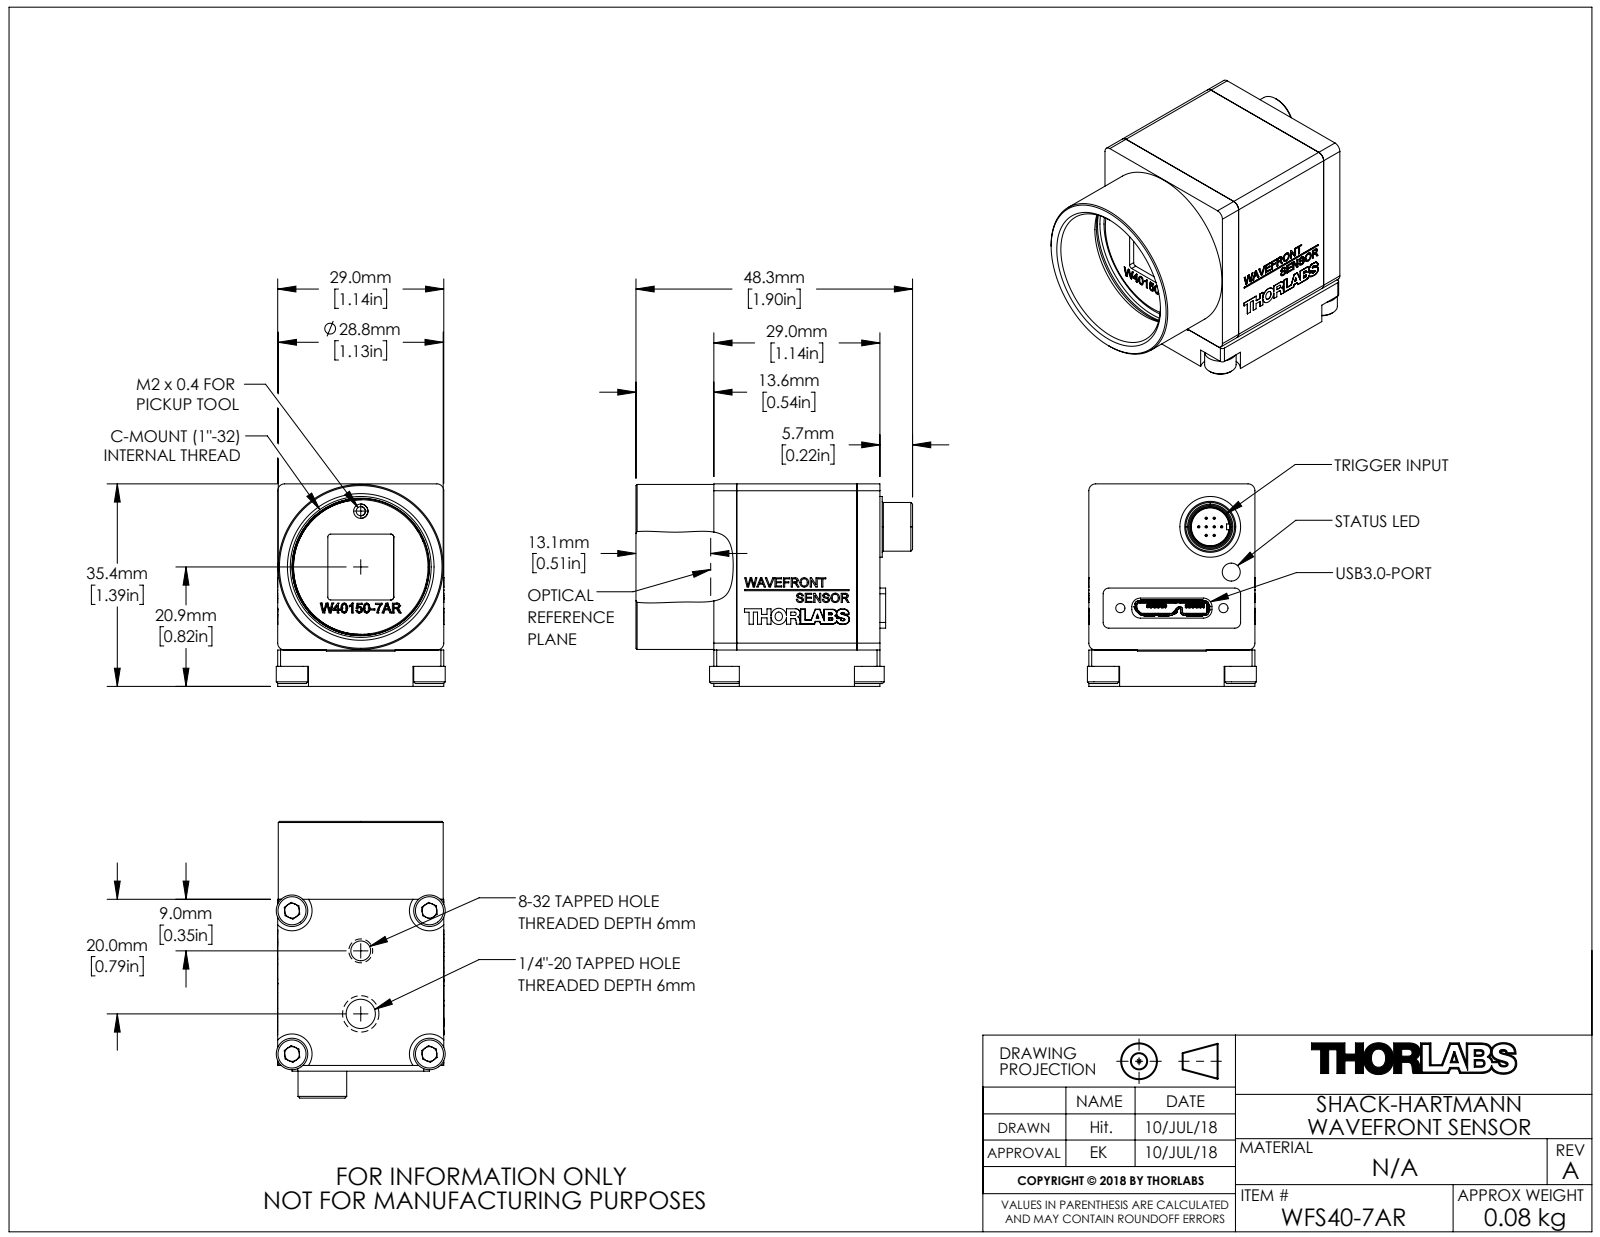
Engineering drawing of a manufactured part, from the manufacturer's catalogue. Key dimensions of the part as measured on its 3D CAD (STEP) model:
Part name (STEP PRODUCT): 20.05.05_MTN008531 WFS40-7AR
STEP written by: SolidWorks 2018 (AUTOMOTIVE_DESIGN)
Units: millimetres
Bodies: 24 solids, 1964 faces (1515 planar, 208 cylindrical, 241 other)
Overall size (bounding box): 48.3 × 35.35 × 29.5
Volume: 18 081 mm³ · Surface area: 20 374 mm²
Round holes (diameter × count): ⌀3.2 ×11, ⌀2.5 ×5, ⌀1.6 ×3, ⌀1.9 ×3, ⌀1 ×1, ⌀1.5 ×1, ⌀3.3 ×1, ⌀5 ×1, ⌀6.8 ×1, ⌀8 ×1, ⌀24 ×1, ⌀24.6 ×1
Round bosses / shafts (diameter × count): ⌀3 ×11, ⌀0.4 ×8, ⌀5.5 ×4, ⌀28.8 ×1, ⌀23.5 ×1, ⌀10.6 ×1, ⌀8.5 ×1
Partial cylindrical surfaces — rounded edges, fillets, slot ends (radius × count): R0.5 ×27, R1 ×12, R1.5 ×10, R0.6 ×8, R1.8 ×8, R0.2 ×7, R0.1 ×6, R1.2 ×6
Main face-to-face distances: 0.6, 29, 28.4, 6.35, 1.2, 1, 16.65, 35.35, 4.8, 27.8
Hole centre spacings: 9.75, 18.83, 9.74, 13.79, 16.88, 5.04, 5.05, 13.89
